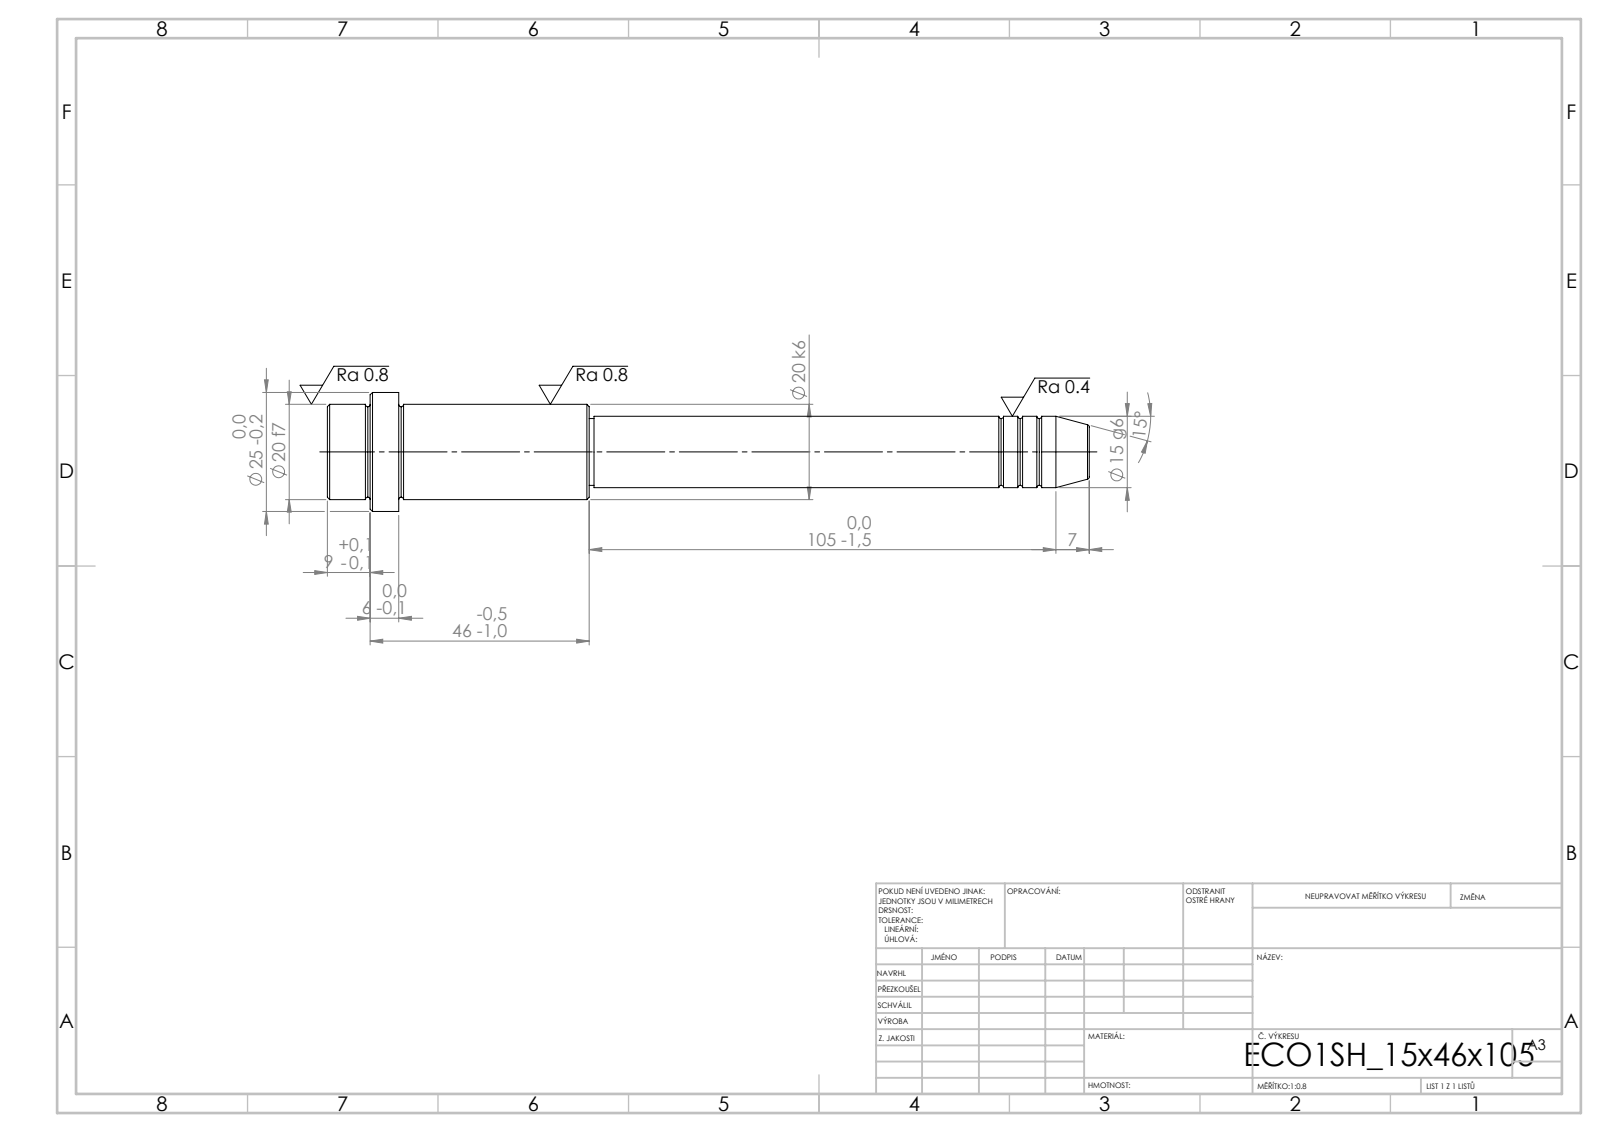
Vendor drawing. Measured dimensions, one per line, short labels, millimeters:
written by: SolidWorks 2019 (CONFIG_CONTROL_DESIGN)
unit: mm
bodies: 1 solid, 52 faces (6 planar, 16 cylindrical, 30 other)
size: 160 × 25 × 25
volume: 36 459 mm³; area: 9 486 mm²
bosses: 1× ⌀25, 1× ⌀20, 1× ⌀15, 1× ⌀14
face distances: 15, 6, 9, 40, 46, 55, 105, 145, 151, 160
